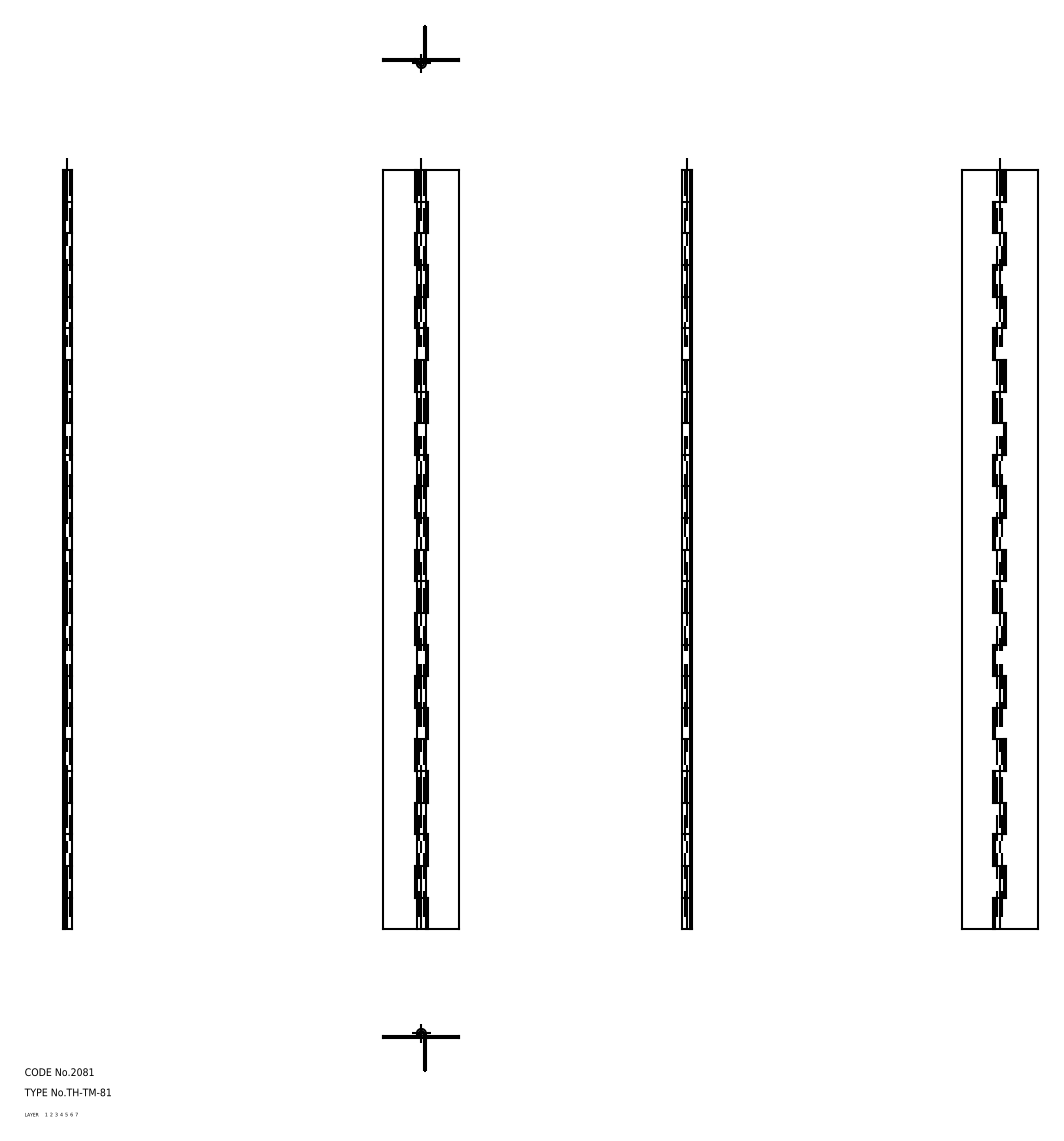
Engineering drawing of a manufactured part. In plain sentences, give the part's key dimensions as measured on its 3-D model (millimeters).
The part is named "hinge piece_B; hinge piece_A; shaft; TH_TM_81_25791_36". Its 3-D file was written by "CADfix (AUTOMOTIVE_DESIGN)". It is 3 solids with 156 faces: 0 planar, 0 cylindrical and 156 other. Overall it measures 300 by 30 by 3.6 millimeters. Its volume is 9 315 cubic millimeters and its surface area 24 198 square millimeters.
